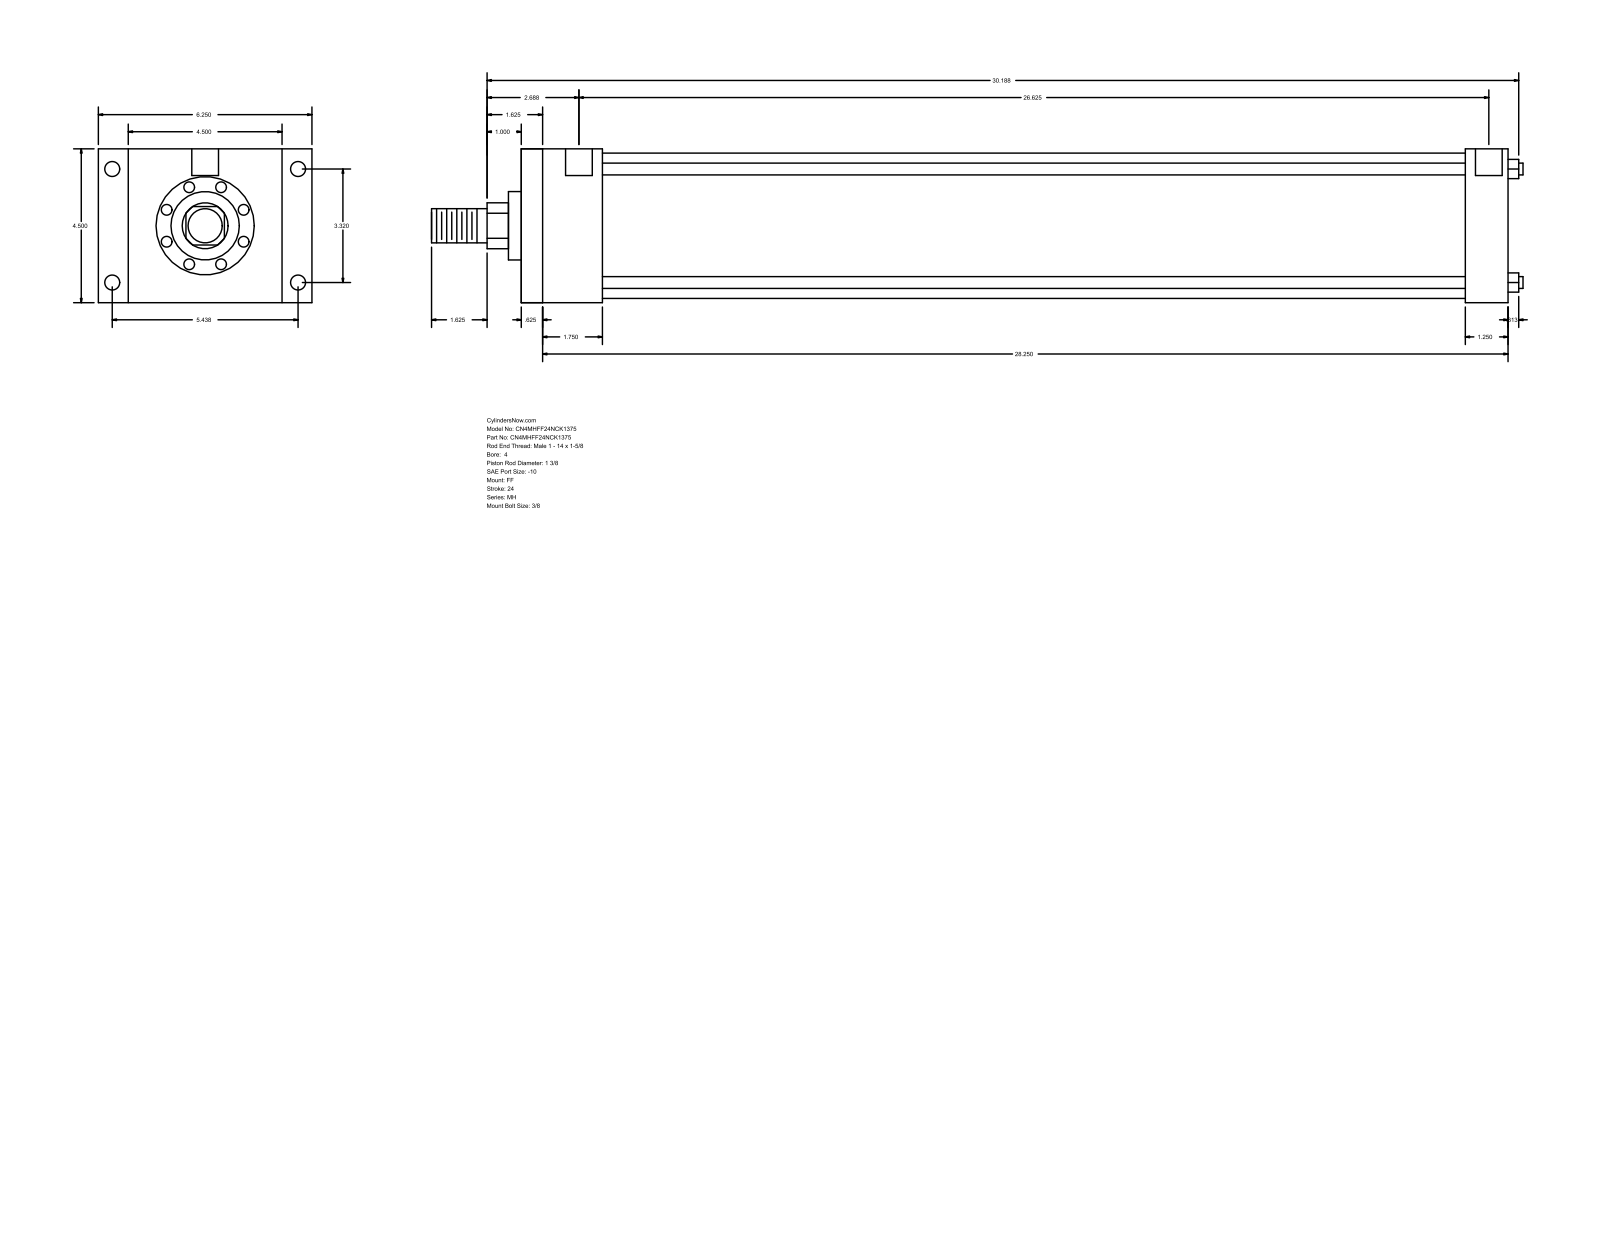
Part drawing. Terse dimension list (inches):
name: MH_FF__0400_1.375
written by: GSSL Pune (CONFIG_CONTROL_DESIGN)
unit: in
bodies: 0 solids, 92 faces (64 planar, 28 cylindrical, 0 other)
size: 31.937 × 6.25 × 4.5
holes: 4× ⌀0.344, 4× ⌀0.438, 2× ⌀0.781
bosses: 4× ⌀0.345, 1× ⌀4.25, 1× ⌀2, 1× ⌀1.375, 1× ⌀1
rounds: 1× R0.672
face distances: 4.5, 28.875, 0.625, 28.25, 2.375, 1.75, 26.5, 27.625, 27, 25.25
hole spacings: 3.32, 5.438, 6.371, 26.75, 0.062, 0.063, 26.625, 26.687
